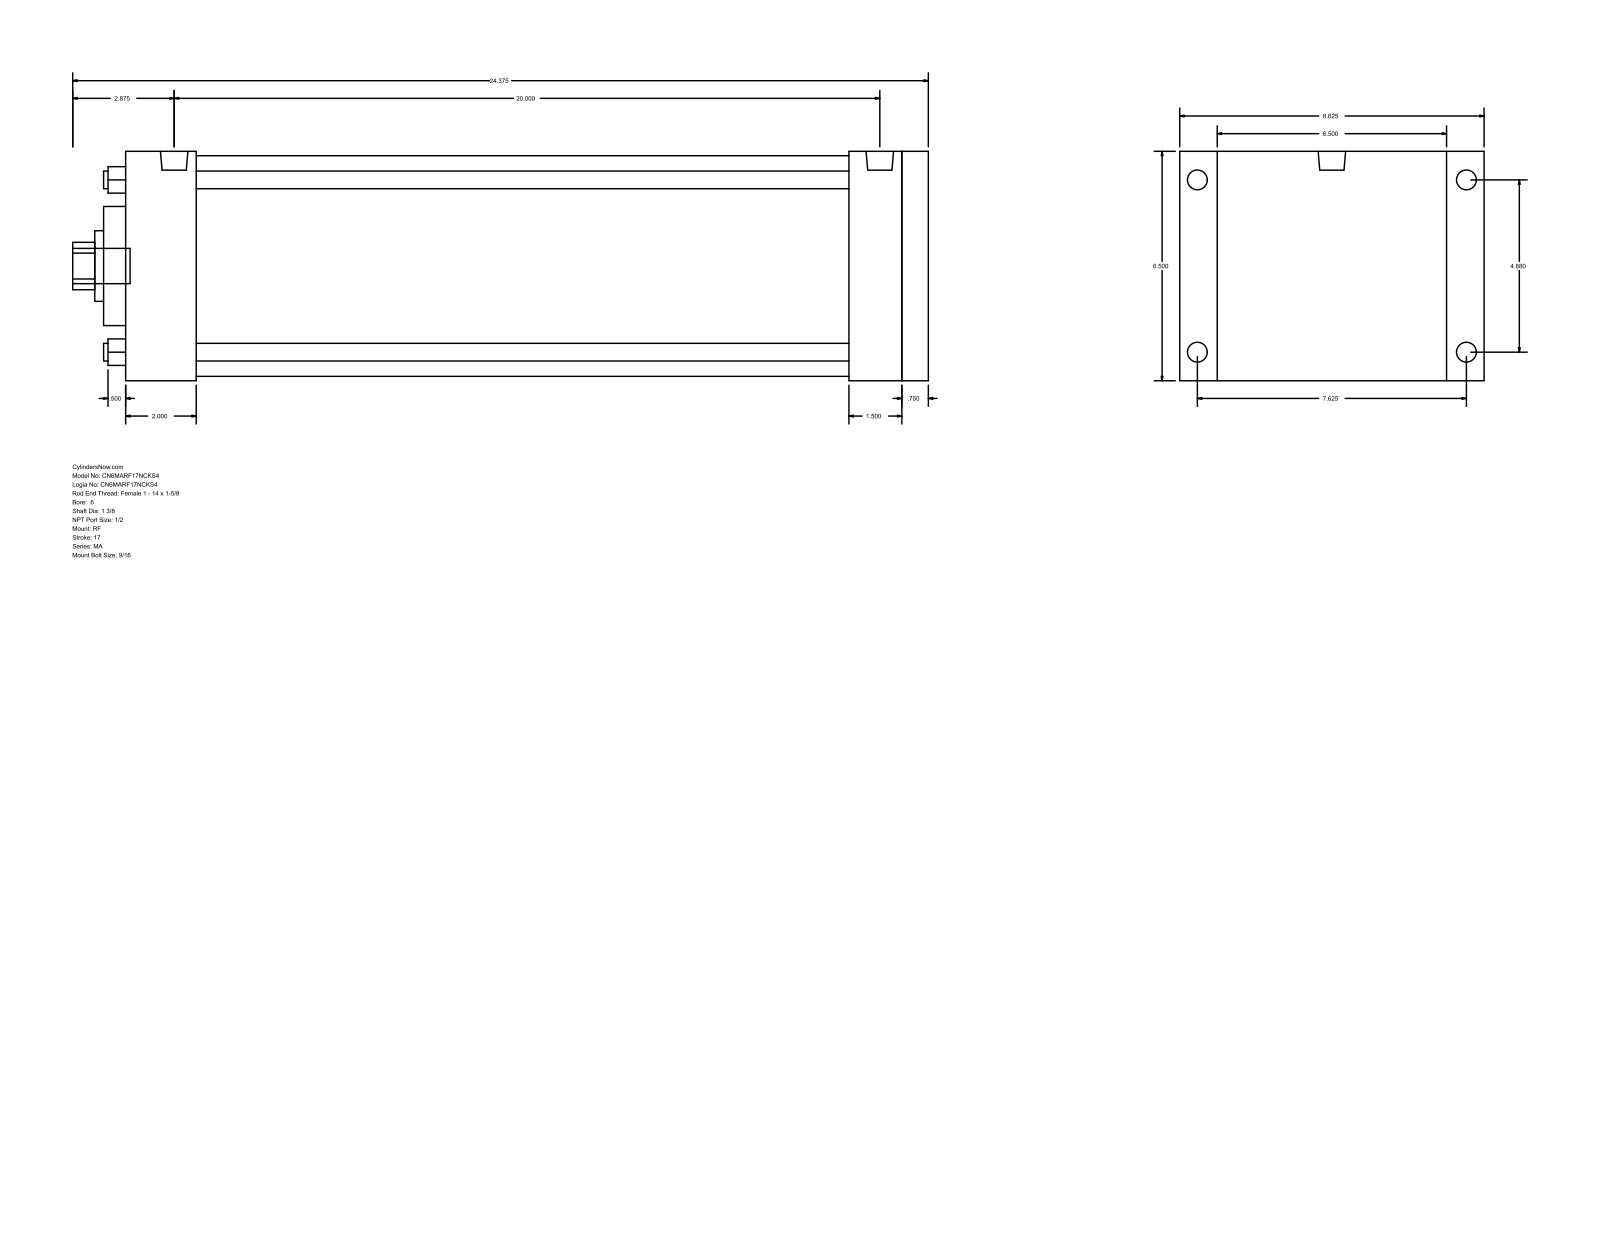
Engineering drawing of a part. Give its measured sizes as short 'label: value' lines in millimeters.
name: MA_RF__0600_1.375
written by: GSSL Pune (CONFIG_CONTROL_DESIGN)
unit: mm
bodies: 0 solids, 94 faces (65 planar, 29 cylindrical, 0 other)
size: 619.12 × 219.07 × 165.1
holes: 4× ⌀12.7, 1× ⌀34.92, 1× ⌀50.8, 1× ⌀85.72, 1× ⌀158.75
bosses: 4× ⌀17.46, 4× ⌀14.29, 2× ⌀19.77, 1× ⌀25.4
rounds: 1× R17.06
face distances: 165.1, 581.02, 19.04, 561.98, 38.1, 50.8, 511.18, 530.22, 523.88, 473.08
hole spacings: 87.65, 123.96, 175.31
